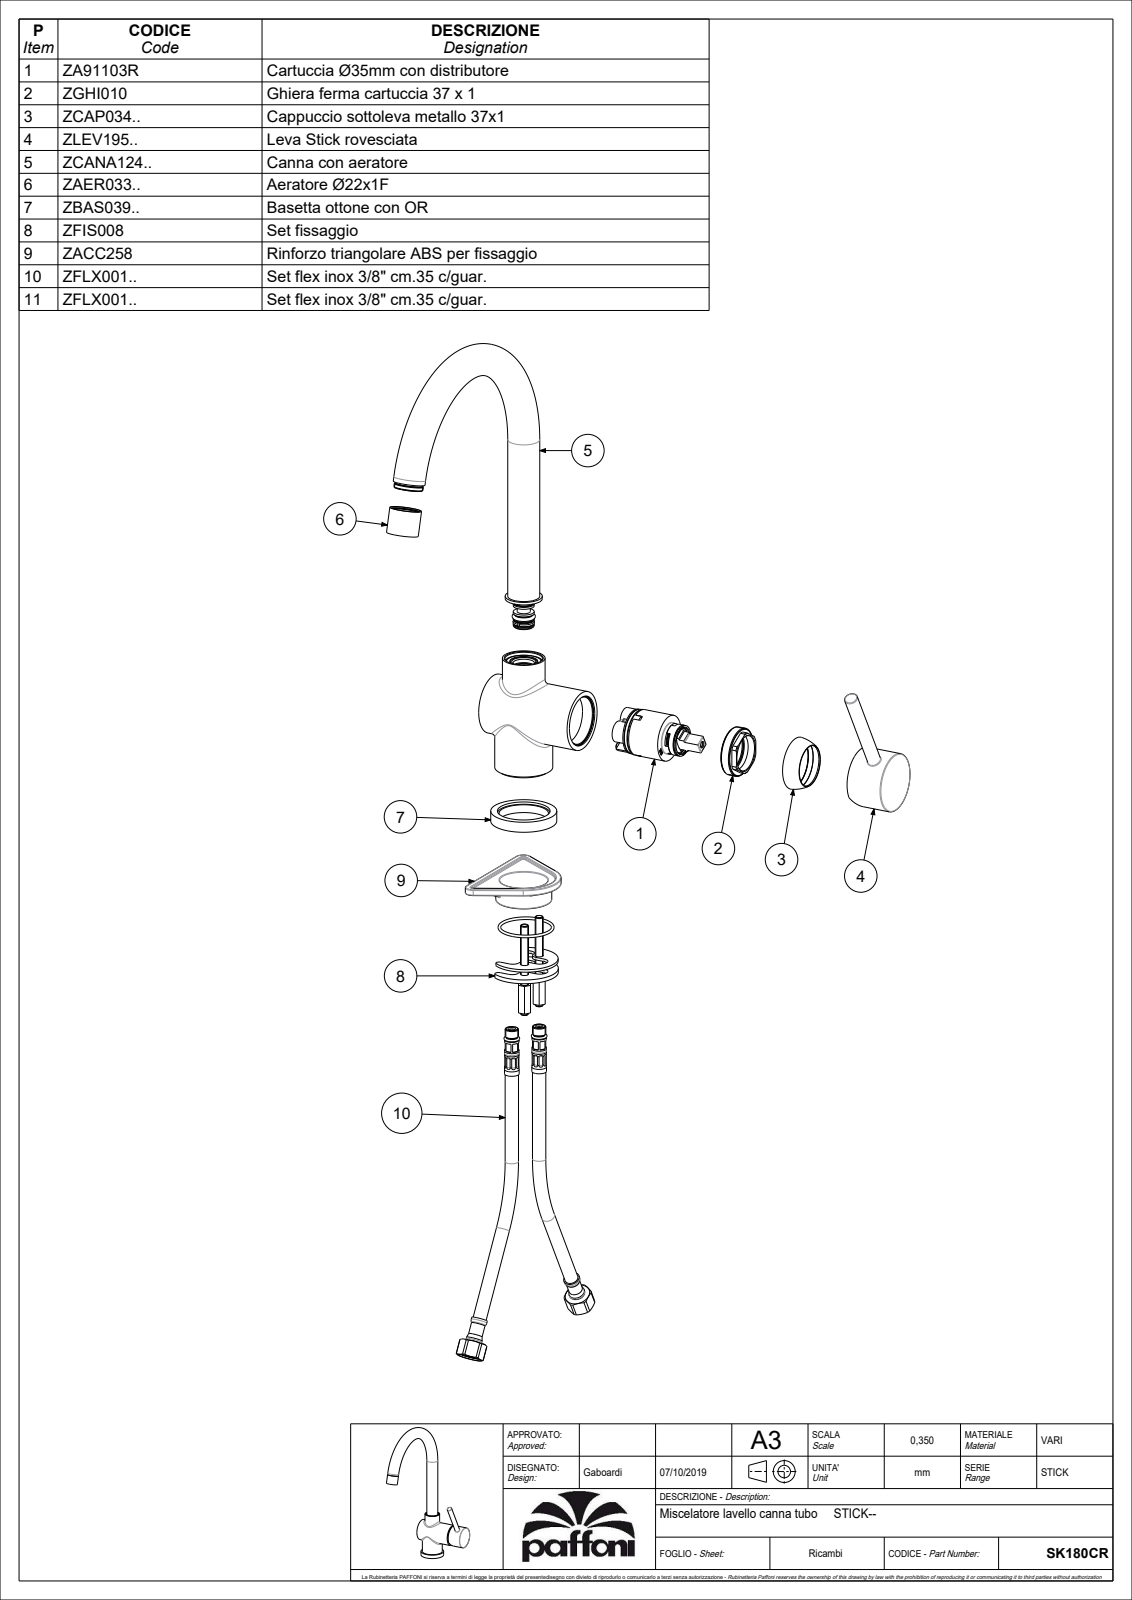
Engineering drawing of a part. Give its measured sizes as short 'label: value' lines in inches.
name: SK180CR
written by: CREO PARAMETRIC BY PTC INC, 2020044 (CONFIG_CONTROL_DESIGN)
unit: in
bodies: 3 solids, 2778 faces (2072 planar, 402 cylindrical, 304 other)
size: 12.539 × 8.392 × 4.256
volume: 13.04 in³; area: 202.7 in²
holes: 5× ⌀0.354, 4× ⌀0.276, 3× ⌀0.157, 3× ⌀0.472, 2× ⌀0.118, 2× ⌀0.217, 2× ⌀0.315, 2× ⌀0.433, 2× ⌀0.63, 2× ⌀0.827, 1× ⌀0.13, 1× ⌀0.177
bosses: 2× ⌀0.945, 2× ⌀0.299, 1× ⌀1.949, 1× ⌀1.772, 1× ⌀1.752, 1× ⌀1.713, 1× ⌀1.524, 1× ⌀1.516
rounds: 52× R0.02, 11× R0.006, 9× R0.012, 5× R0.059, 4× R0.039, 4× R0.276, 2× R0.177, 2× R0.197
face distances: 0.059, 0.256, 0.039, 0.118, 0.098, 0.02, 0.394, 0.079, 4.083, 0.472
hole spacings: 0.513, 0.028, 0.335, 0.339, 0.378, 0.52, 0.53, 0.532
